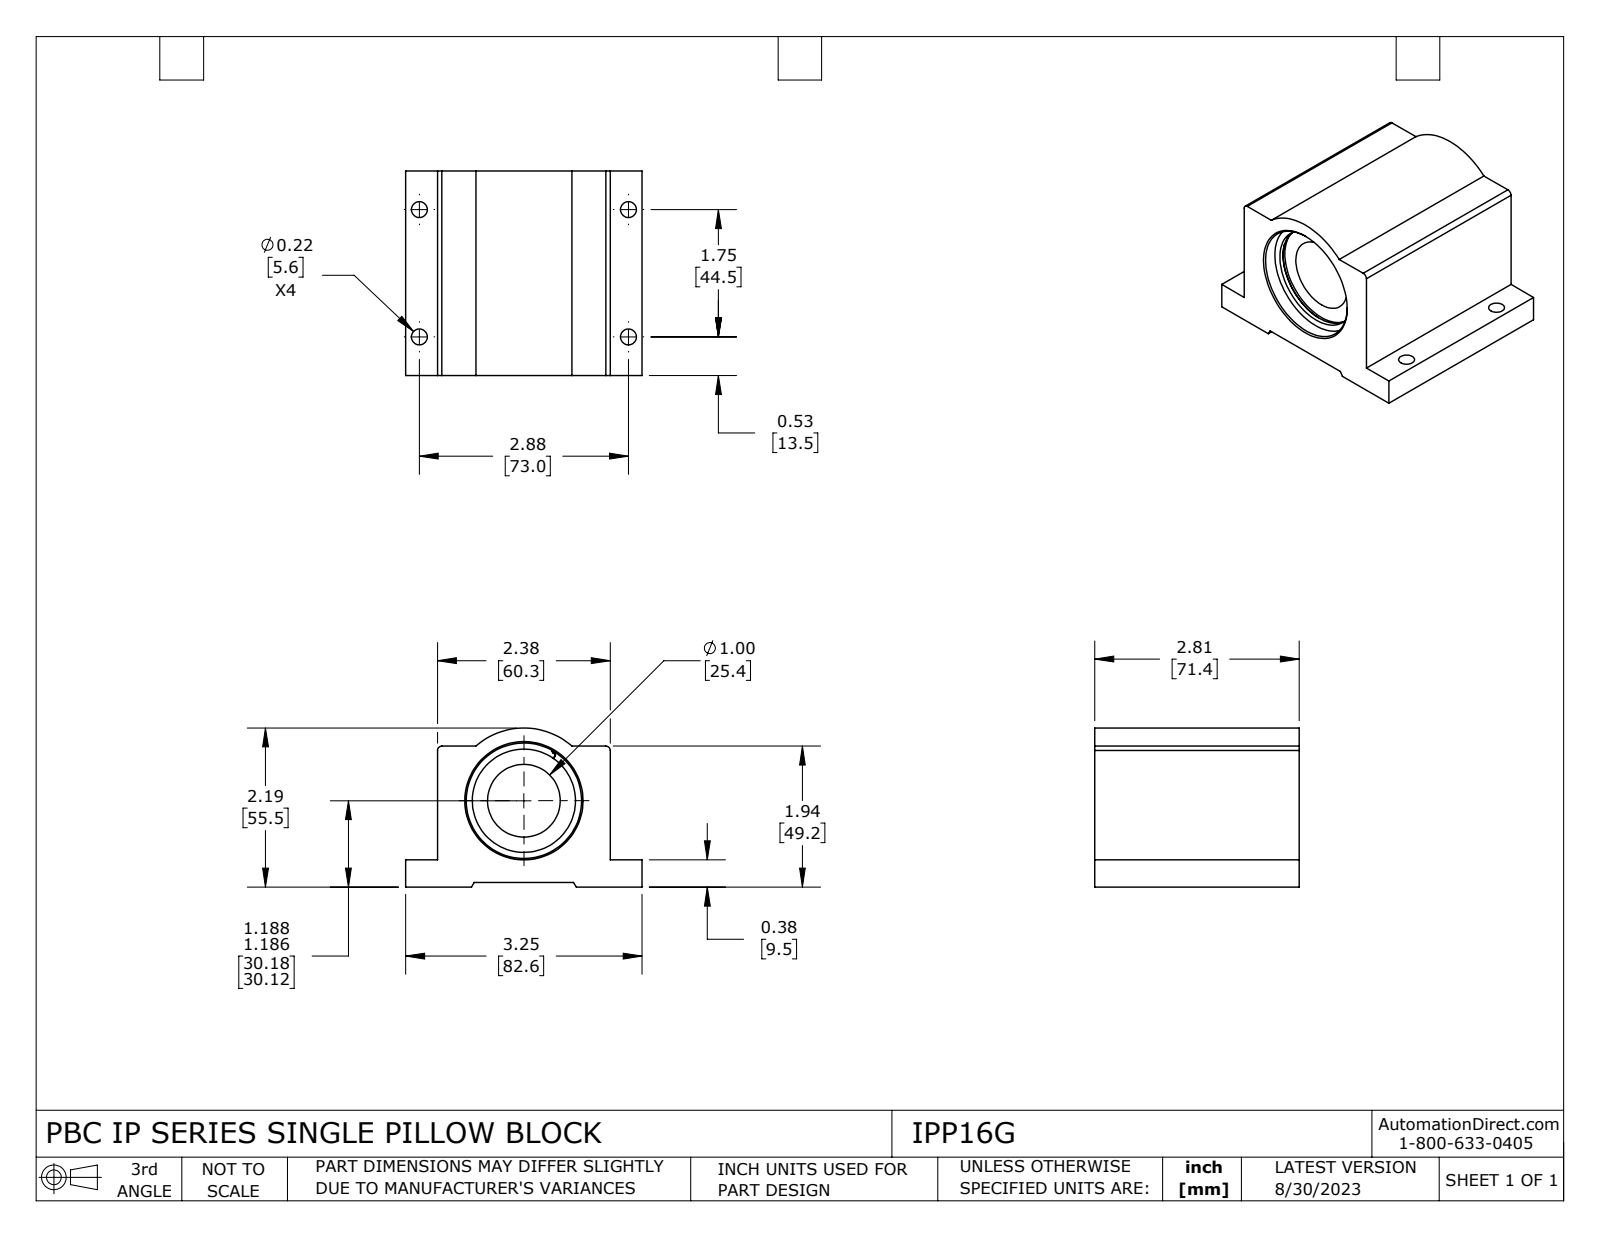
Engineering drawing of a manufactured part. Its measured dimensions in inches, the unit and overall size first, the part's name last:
Units: inches
Overall size (bounding box): 3.25 × 2.813 × 2.187
Round holes (diameter × count): ⌀0.219 ×4, ⌀1 ×1, ⌀1.419 ×1, ⌀1.427 ×1, ⌀1.586 ×1, ⌀1.671 ×1
Round bosses / shafts (diameter × count): ⌀1.675 ×1, ⌀1.563 ×1, ⌀1.469 ×1
Partial cylindrical surfaces — rounded edges, fillets, slot ends (radius × count): R0.021 ×4, R0.016 ×2, R0.026 ×2, R0.06 ×2, R1 ×1
Main face-to-face distances: 2.375, 0.065, 1.938, 2.813, 1.873, 0.375, 0.31, 1.563, 0.437, 2.812
Hole centre spacings: 1.75, 2.875, 3.366
Volume: 11.15 in³ · Surface area: 76.09 in²
Bodies: 4 solids, 126 faces (43 planar, 63 cylindrical, 20 other)
Part name (STEP PRODUCT): IPP16G
STEP written by: SolidWorks 2021 (CONFIG_CONTROL_DESIGN)
